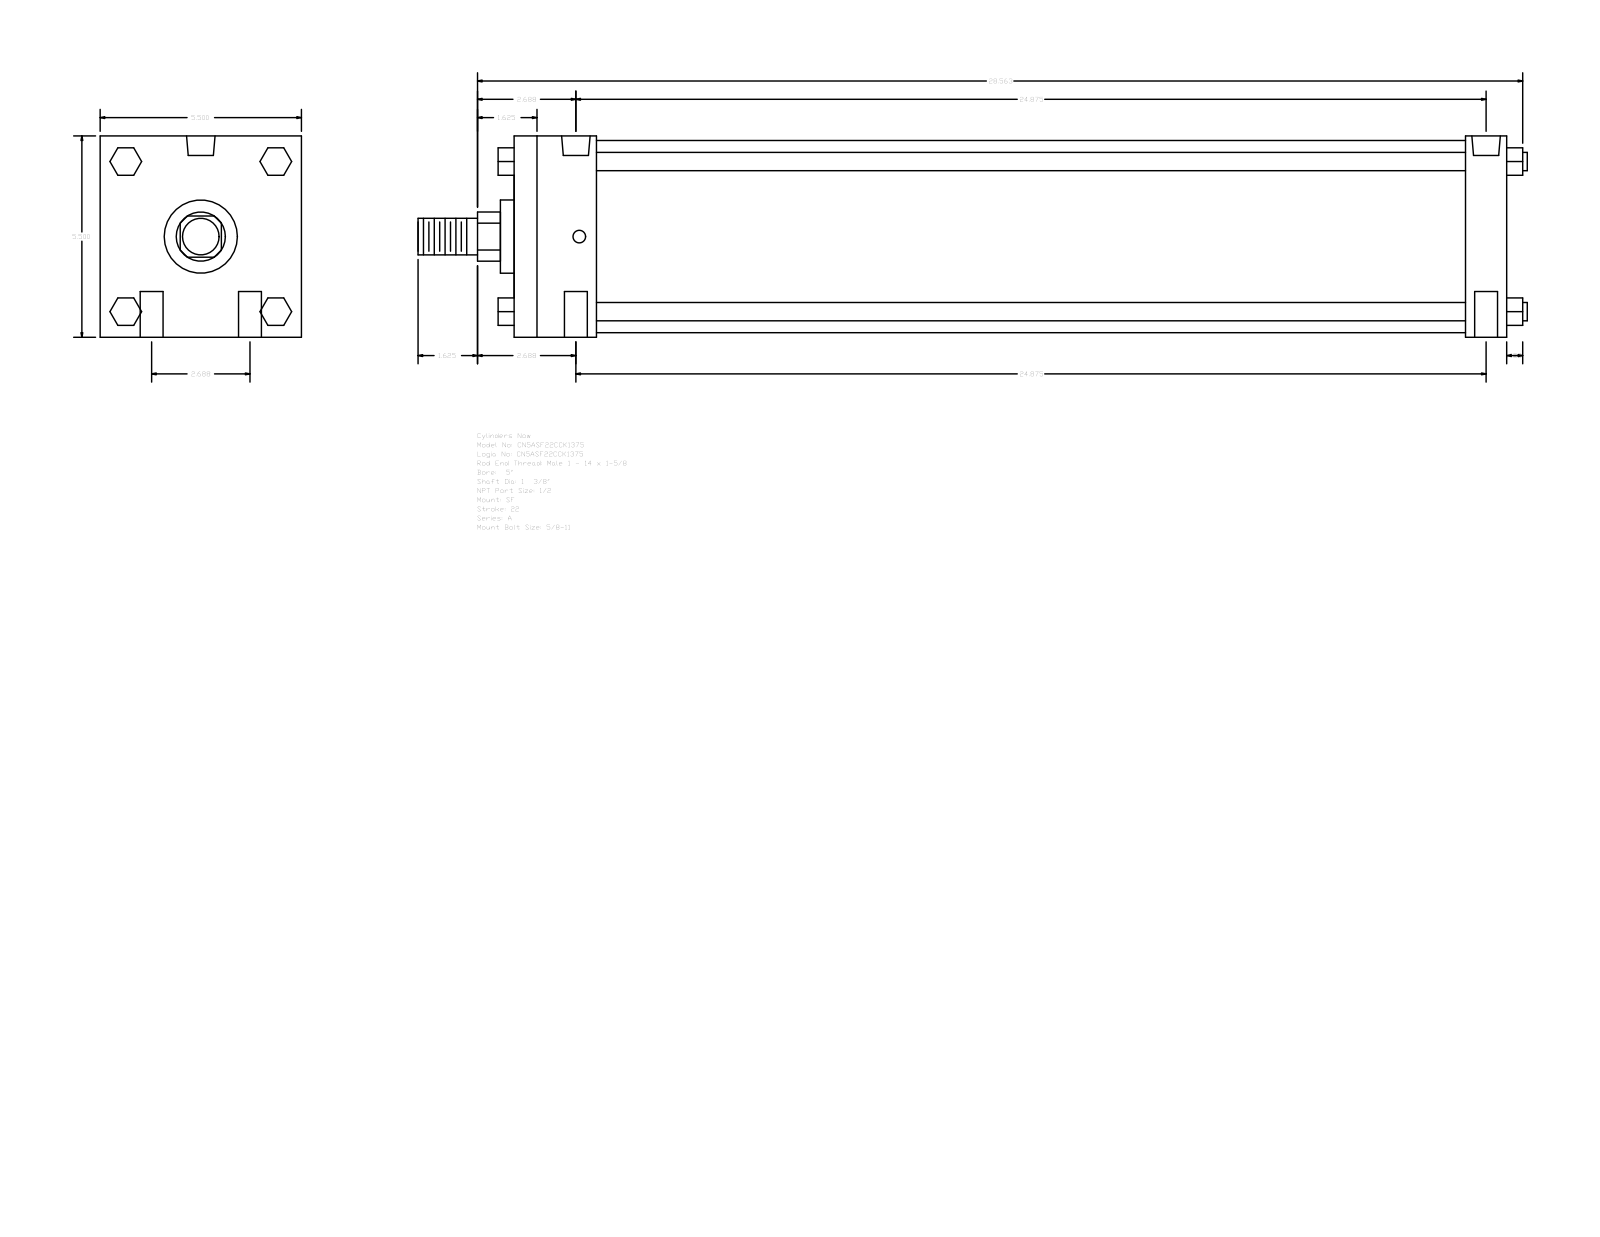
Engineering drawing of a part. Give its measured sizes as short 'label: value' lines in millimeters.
name: A_SF__0500_1.375
written by: GSSL Pune (CONFIG_CONTROL_DESIGN)
unit: mm
bodies: 0 solids, 124 faces (94 planar, 30 cylindrical, 0 other)
size: 769.94 × 139.7 × 139.7
holes: 4× ⌀15.88, 2× ⌀8.73, 2× ⌀19.77
bosses: 4× ⌀12.7, 1× ⌀133.35, 1× ⌀50.8, 1× ⌀34.92, 1× ⌀25.4
rounds: 1× R17.06
face distances: 139.7, 688.98, 57.15, 28.58, 660.4, 603.25, 631.83, 19.05, 52.07, 90.18
hole spacings: 34.13, 632.75, 631.83, 68.26, 635.51, 627.05
